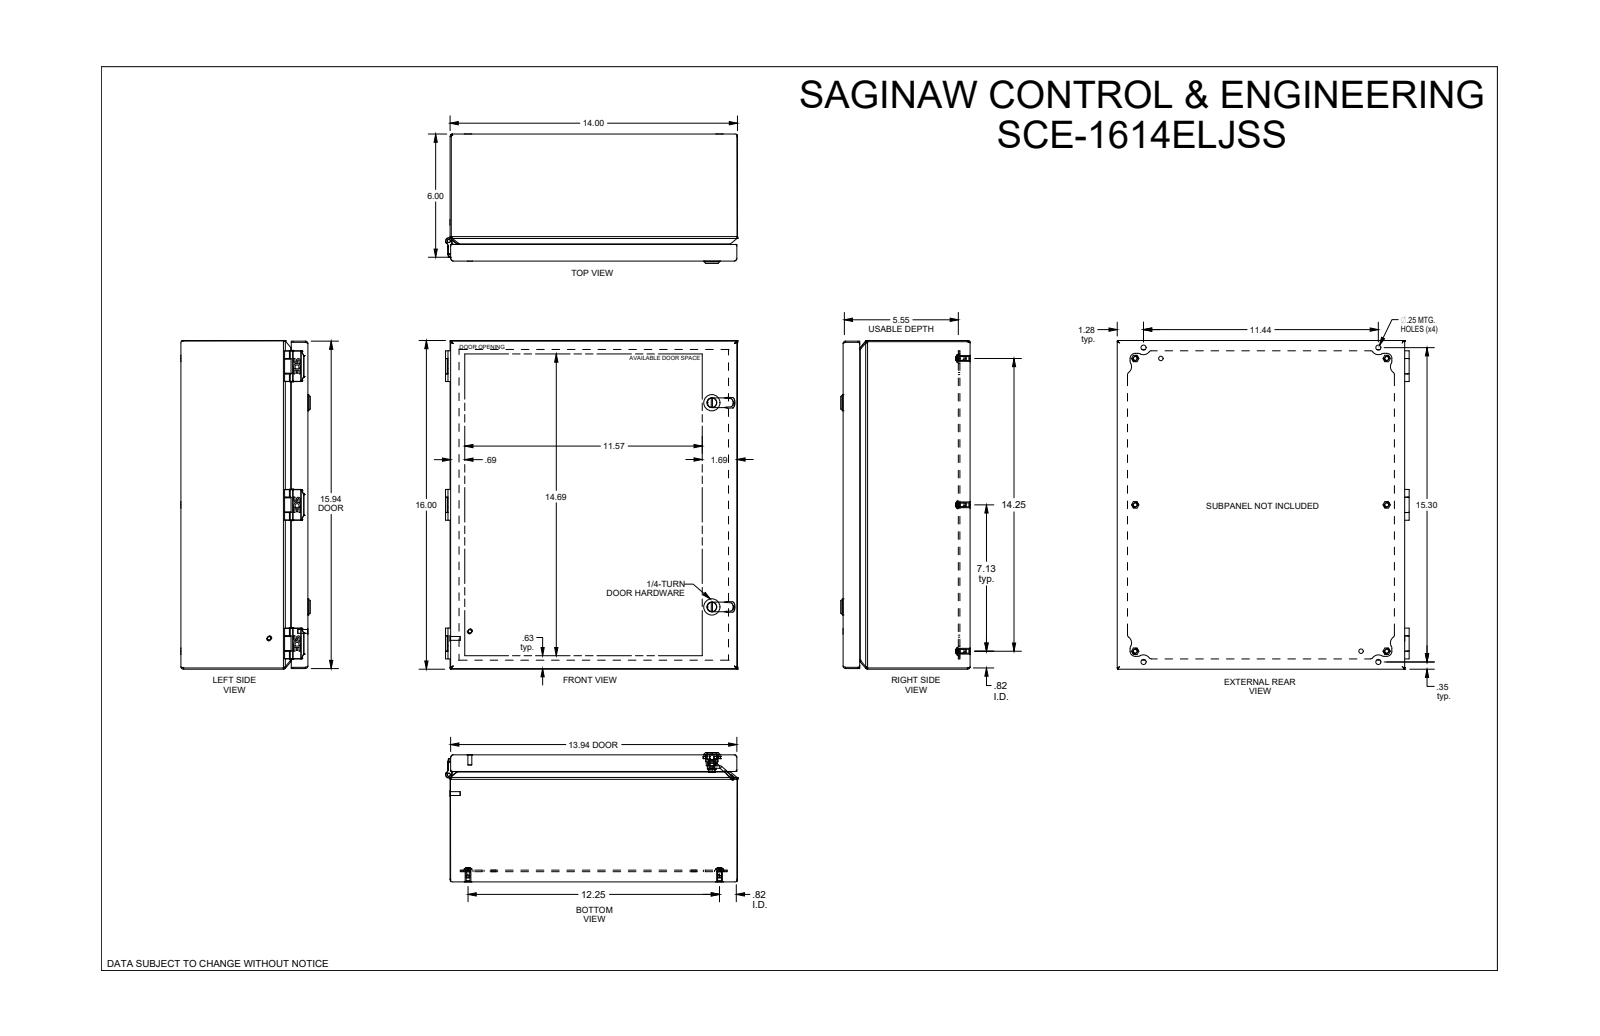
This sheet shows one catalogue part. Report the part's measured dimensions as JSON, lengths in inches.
{"part_name": "SCE-1614ELJ", "step_written_by": "SolidWorks 2019 (AUTOMOTIVE_DESIGN)", "units": "inches", "bodies": {"solids": 41, "faces": 2584, "planar": 713, "cylindrical": 682, "other": 1189}, "overall_size": [16.06, 14.22, 6.296], "volume_in3": 69.94, "surface_area_in2": 2197, "round_holes": [[0.17, 6], [0.19, 6], [0.25, 6], [0.284, 4], [0.266, 3], [0.2, 2], [0.218, 2], [0.239, 2], [0.254, 2], [0.269, 2], [0.282, 2], [0.326, 2]], "round_bosses_or_shafts": [[0.188, 8], [0.479, 6], [0.373, 6], [0.28, 6], [0.788, 2], [0.548, 2], [0.46, 2], [0.43, 2]], "partial_cylinders_radius": [[0.106, 198], [0.005, 114], [0.025, 36], [0.03, 16], [0.05, 16], [0.01, 14], [0.25, 13], [0.06, 12]], "face_to_face_distances": [0.059, 0.06, 6.185, 6.126, 6.066, 6.125, 0.571, 0.512, 5.554, 5.614], "hole_center_spacings": [6.75, 7.125, 14.171, 12.25, 13.5, 14.311, 0.06, 1.25]}
